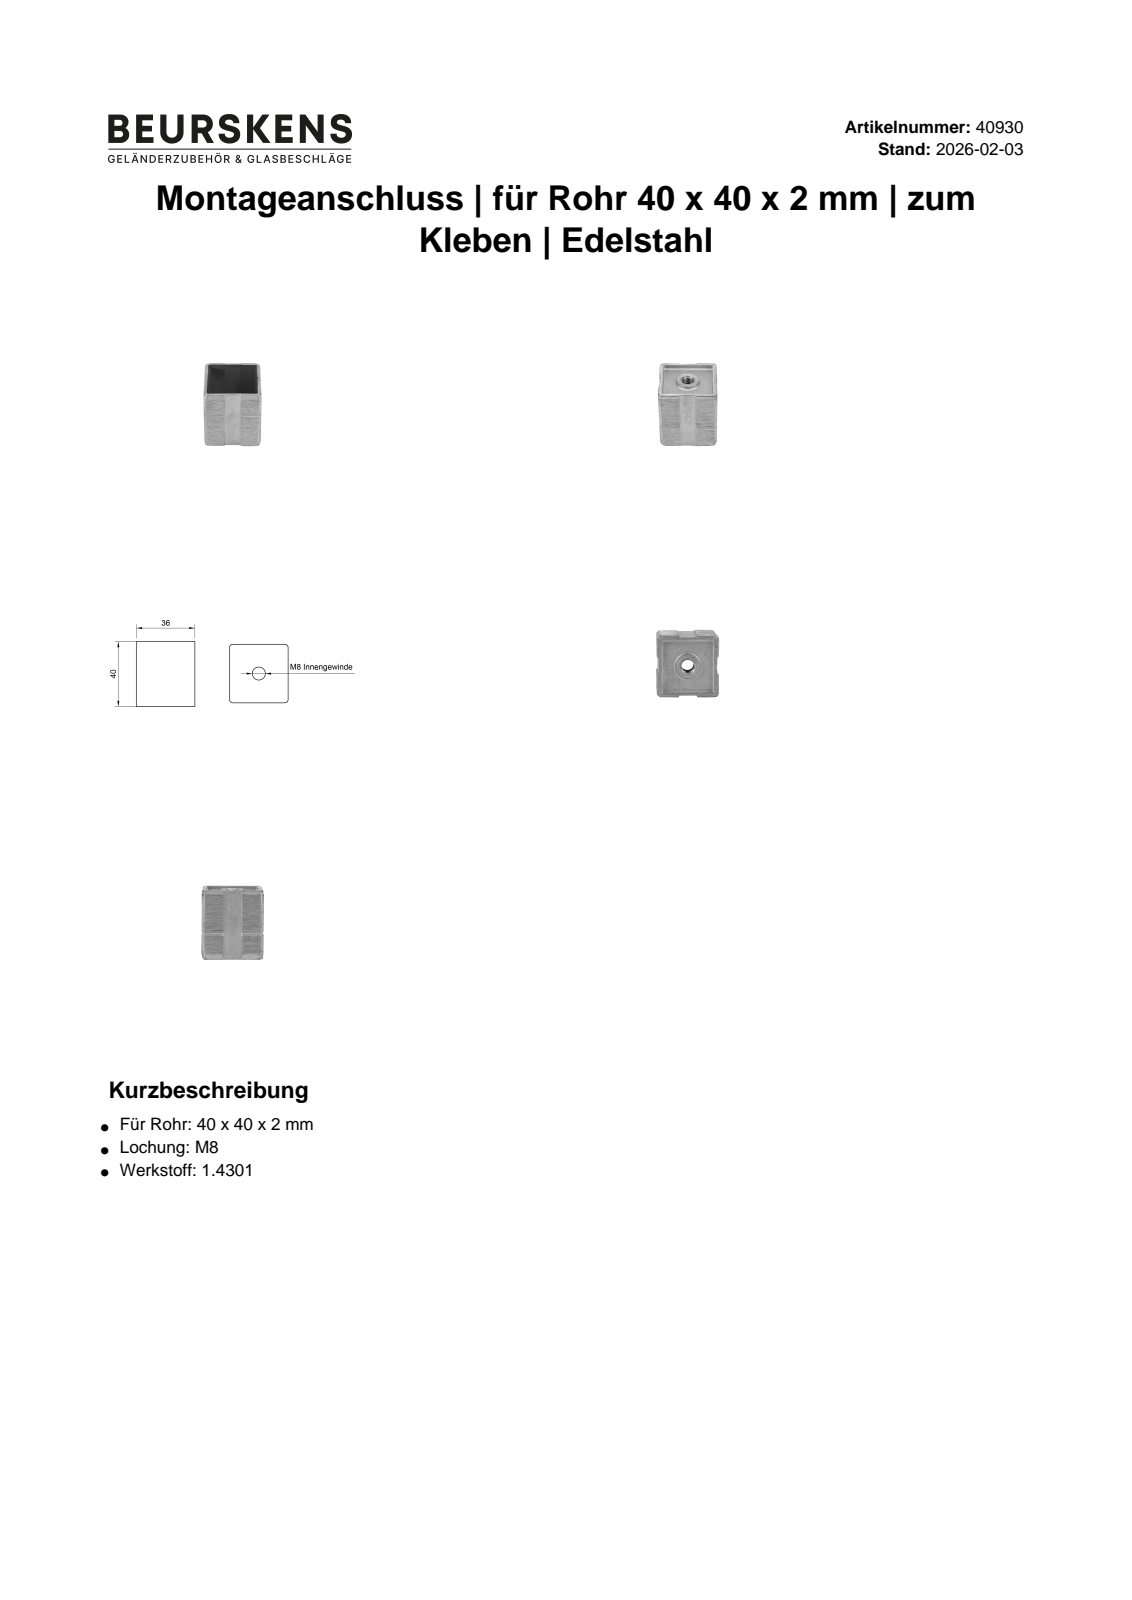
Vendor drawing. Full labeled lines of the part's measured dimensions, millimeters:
Part name (STEP PRODUCT): 40930
STEP written by: Autodesk Inventor 2022 (AUTOMOTIVE_DESIGN)
Units: millimetres
Bodies: 1 solid, 18 faces (12 planar, 6 cylindrical, 0 other)
Overall size (bounding box): 40 × 36 × 36
Volume: 22 078 mm³ · Surface area: 13 898 mm²
Round holes (diameter × count): ⌀8 ×1
Round bosses / shafts (diameter × count): ⌀20 ×1
Partial cylindrical surfaces — rounded edges, fillets, slot ends (radius × count): R2 ×4
Main face-to-face distances: 3, 33, 36, 30, 40, 37, 17.5, 14.5, 22.5
